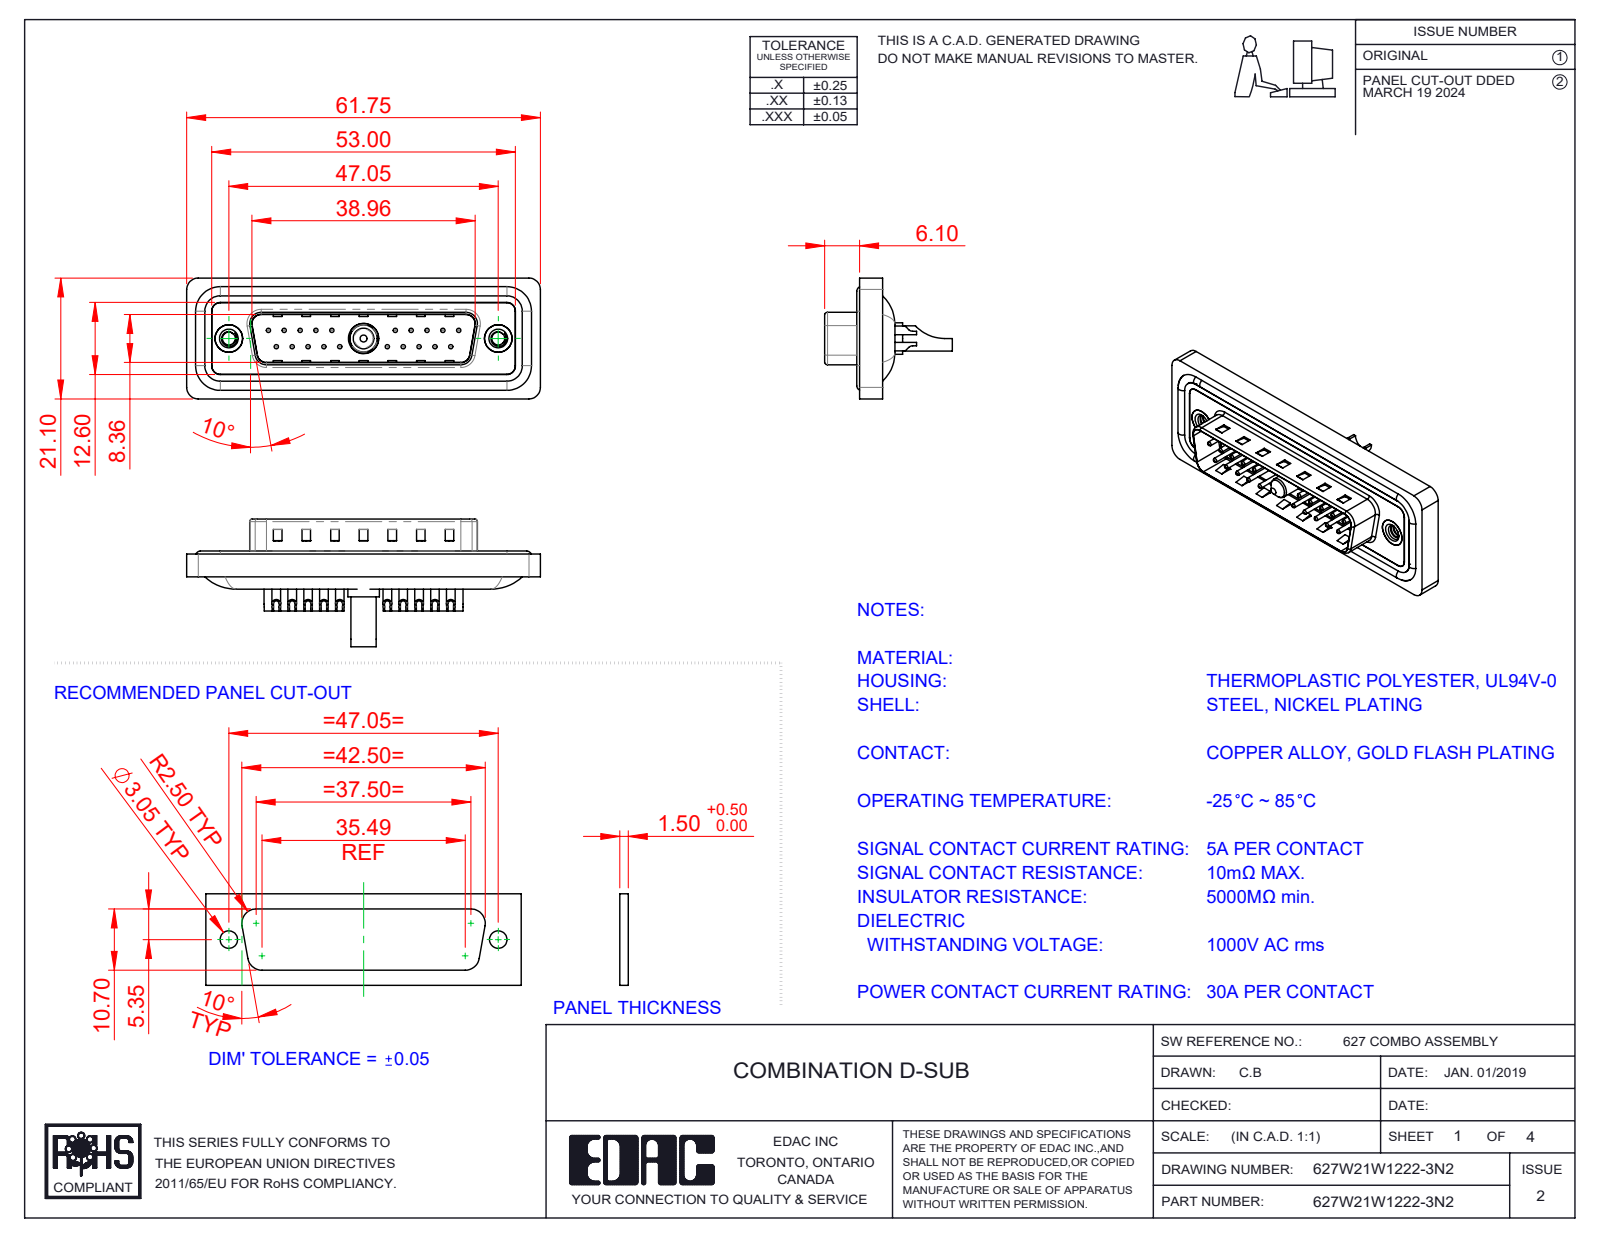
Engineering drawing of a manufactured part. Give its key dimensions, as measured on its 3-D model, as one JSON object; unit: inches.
{"part_name": "627Combo Shell Front_25 Contacts; Power Pin_30A SC; 627Combo Waterproof Housing_25 Contacts; 627Combo Shell Rear_25 Contacts (+5 more)", "step_written_by": "SolidWorks 2023 (CONFIG_CONTROL_DESIGN)", "units": "inches", "bodies": {"solids": 29, "faces": 1268, "planar": 402, "cylindrical": 530, "other": 336}, "overall_size": [2.431, 0.878, 0.831], "volume_in3": 0.443, "surface_area_in2": 18.94, "round_holes": [[0.03, 20], [0.039, 20], [0.063, 20], [0.079, 20], [0.089, 2], [0.157, 2], [0.189, 2], [0.197, 2], [0.138, 1], [0.191, 1], [0.209, 1]], "round_bosses_or_shafts": [[0.059, 20], [0.063, 4], [0.193, 2], [0.217, 1], [0.205, 1], [0.187, 1], [0.173, 1], [0.148, 1]], "partial_cylinders_radius": [[0.059, 22], [0.079, 18], [0.02, 8], [0.063, 8], [0.039, 6], [0.01, 4], [0.024, 4], [0.026, 4]], "face_to_face_distances": [0.016, 0.059, 0.043, 0.063, 0.02, 0.122, 0.114, 0.161, 0.032, 0.377], "hole_center_spacings": [0.124, 0.109, 0.218, 0.327, 0.198, 0.763, 0.826, 0.872]}
